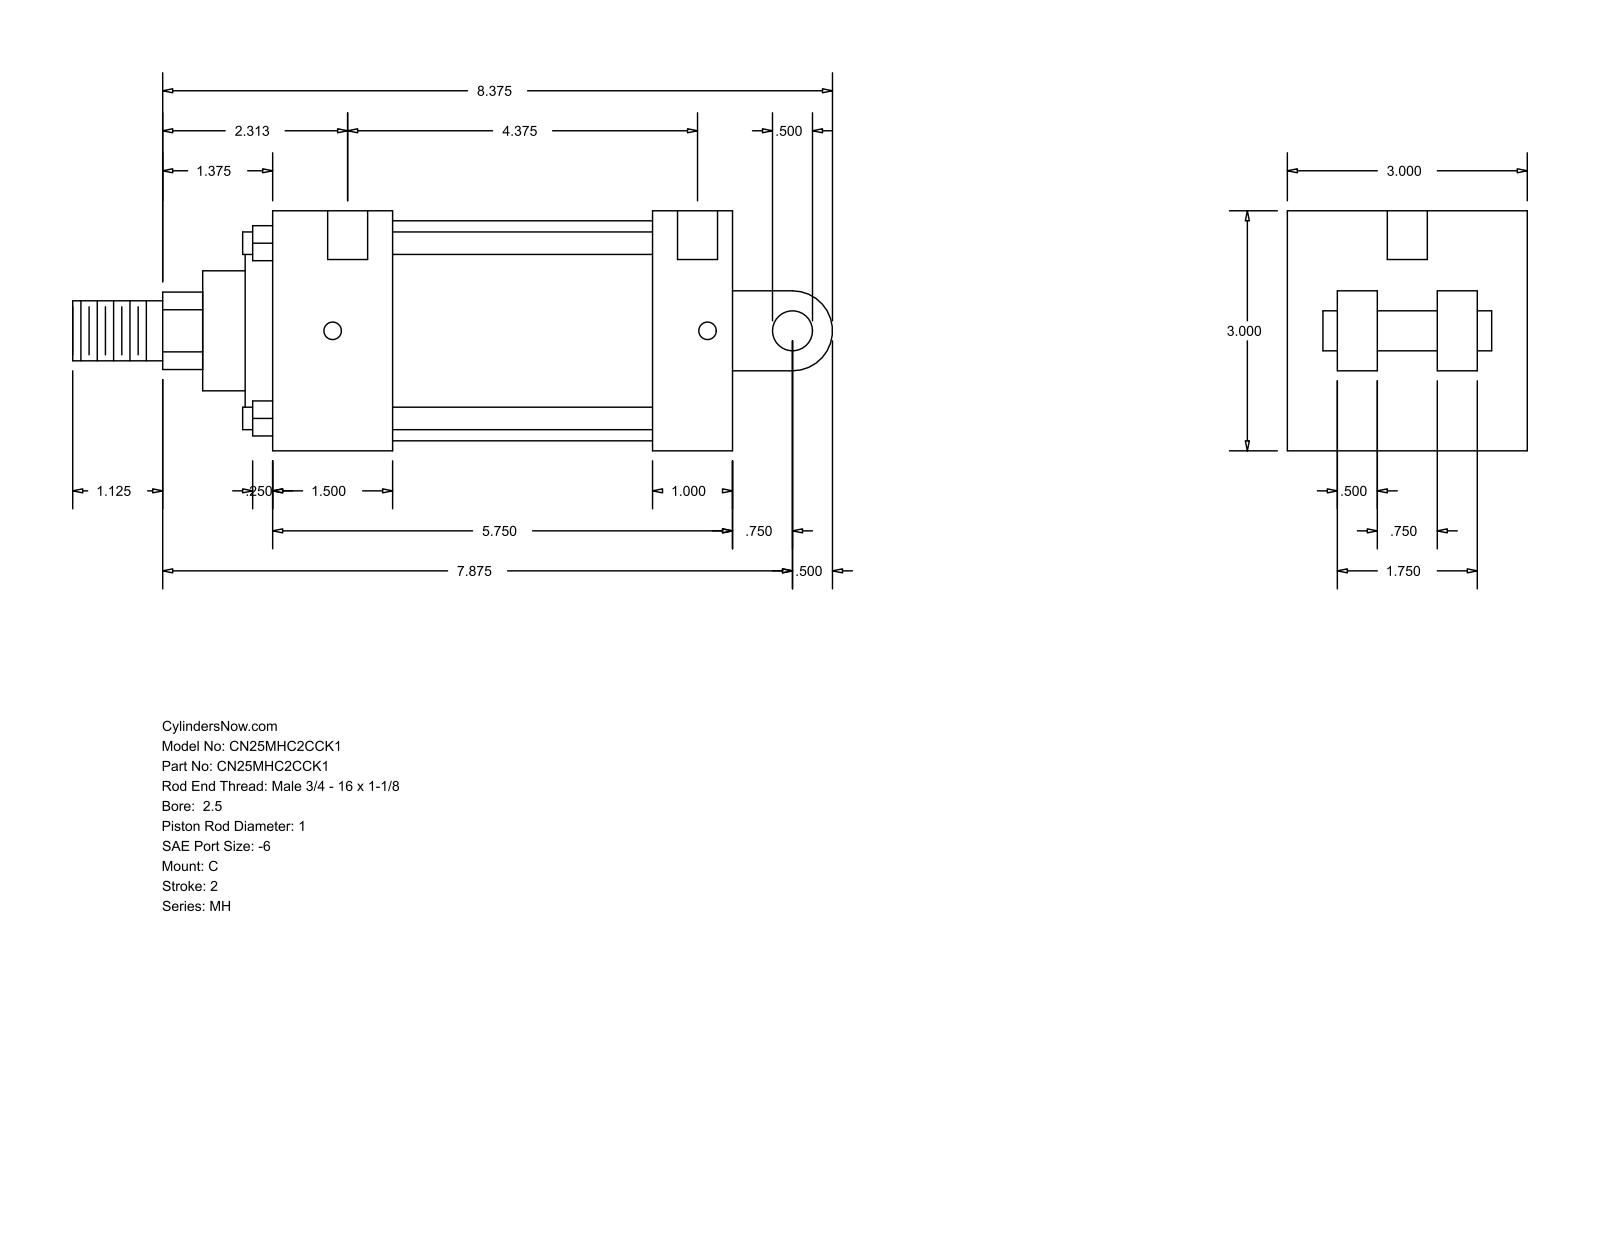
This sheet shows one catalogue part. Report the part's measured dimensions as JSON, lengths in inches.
{"part_name": "MH_C__0250_1", "step_written_by": "GSSL Pune (CONFIG_CONTROL_DESIGN)", "units": "inches", "bodies": {"solids": 0, "faces": 101, "planar": 71, "cylindrical": 30, "other": 0}, "overall_size": [9.5, 3, 3], "round_holes": [[0.219, 4], [0.5, 2]], "round_bosses_or_shafts": [[0.281, 4], [2.75, 1], [2.375, 1], [1.5, 1], [1, 1], [0.75, 1], [0.5, 1]], "partial_cylinders_radius": [[0.484, 1], [0.5, 1]], "face_to_face_distances": [3, 1, 5.75, 2.375, 0.625, 4.75, 1.5, 3.25, 4.25, 0.5], "hole_center_spacings": [4.687, 0.125, 0.187, 4.375, 4.5, 4.562]}
